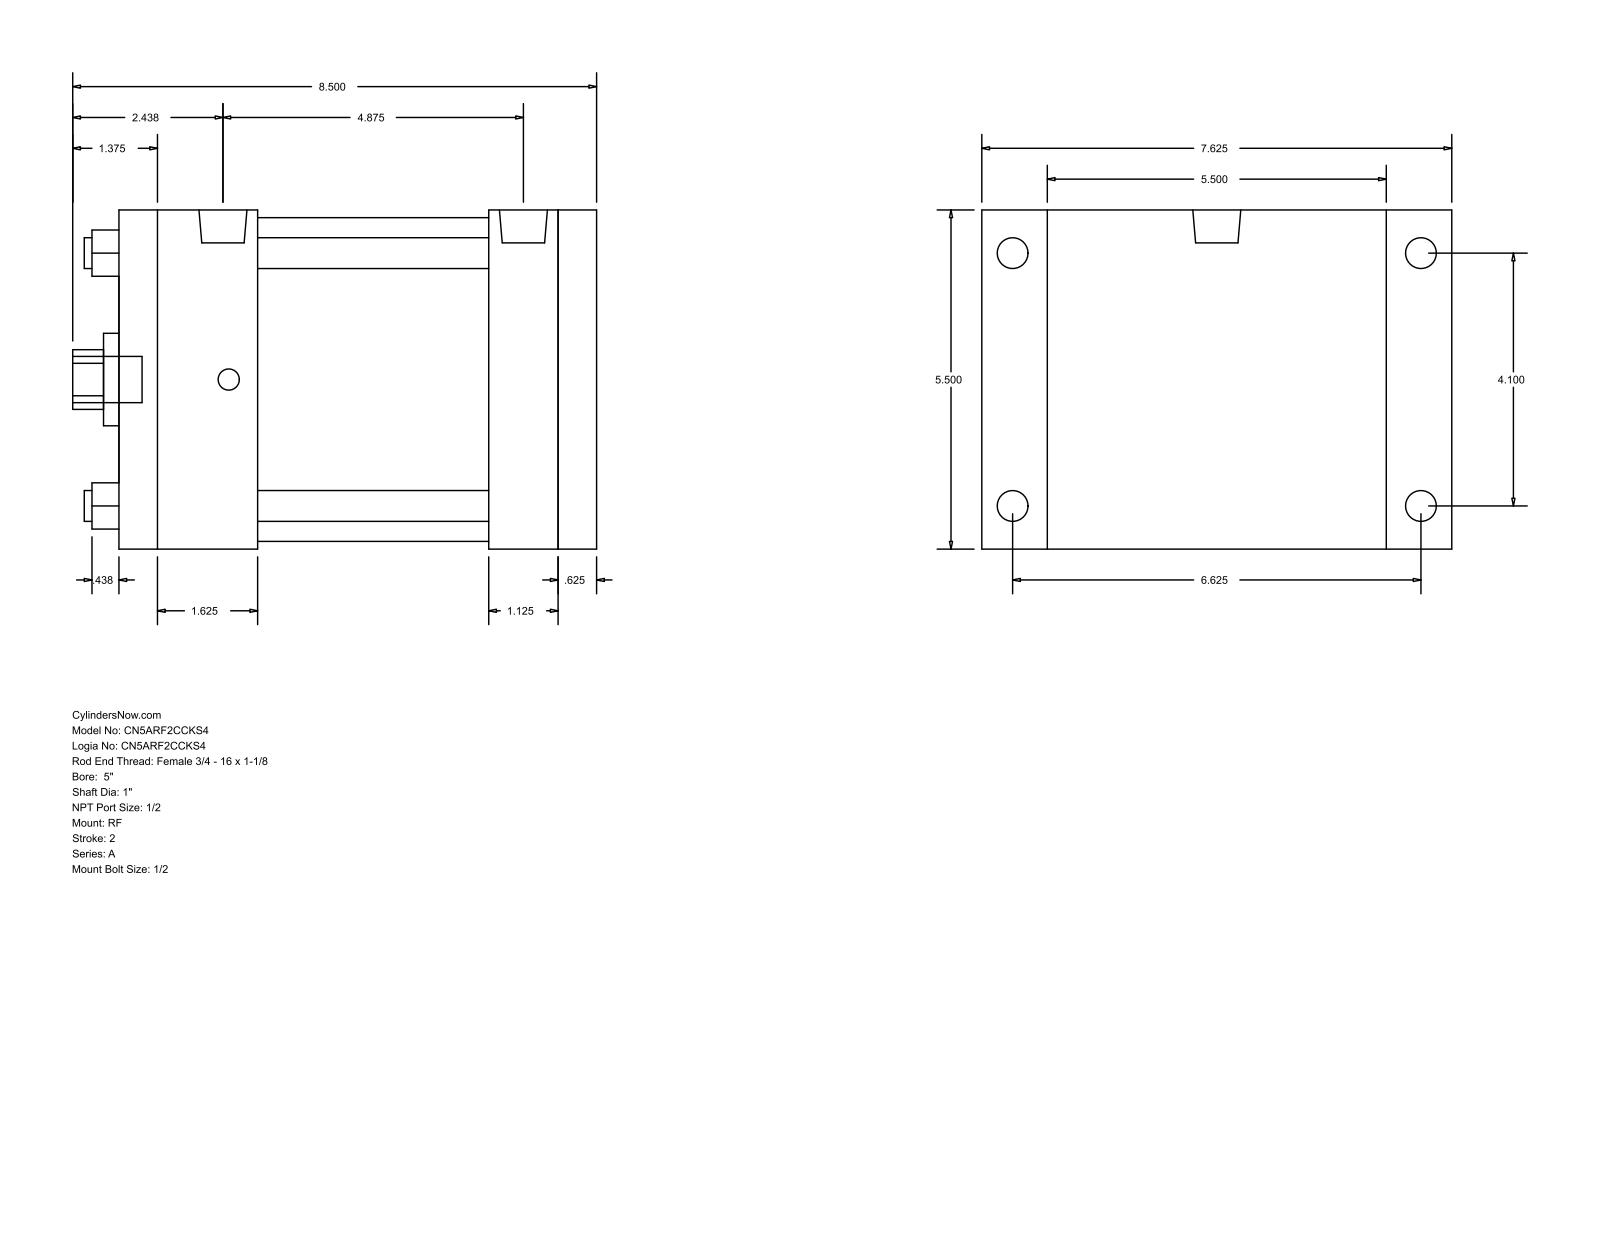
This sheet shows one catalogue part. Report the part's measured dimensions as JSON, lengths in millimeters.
{"part_name": "A_RF__0500_1", "step_written_by": "GSSL Pune (CONFIG_CONTROL_DESIGN)", "units": "millimeters", "bodies": {"solids": 0, "faces": 92, "planar": 64, "cylindrical": 28, "other": 0}, "overall_size": [215.9, 193.68, 139.7], "round_holes": [[12.7, 4], [25.4, 1], [38.1, 1], [133.35, 1]], "round_bosses_or_shafts": [[12.7, 4], [8.73, 4], [19.77, 2], [19.05, 1]], "partial_cylinders_radius": [[12.29, 1]], "face_to_face_distances": [139.7, 196.85, 15.87, 180.98, 57.15, 123.83, 152.4, 95.25, 28.58, 44.45], "hole_center_spacings": [73.64, 104.14, 147.28]}
